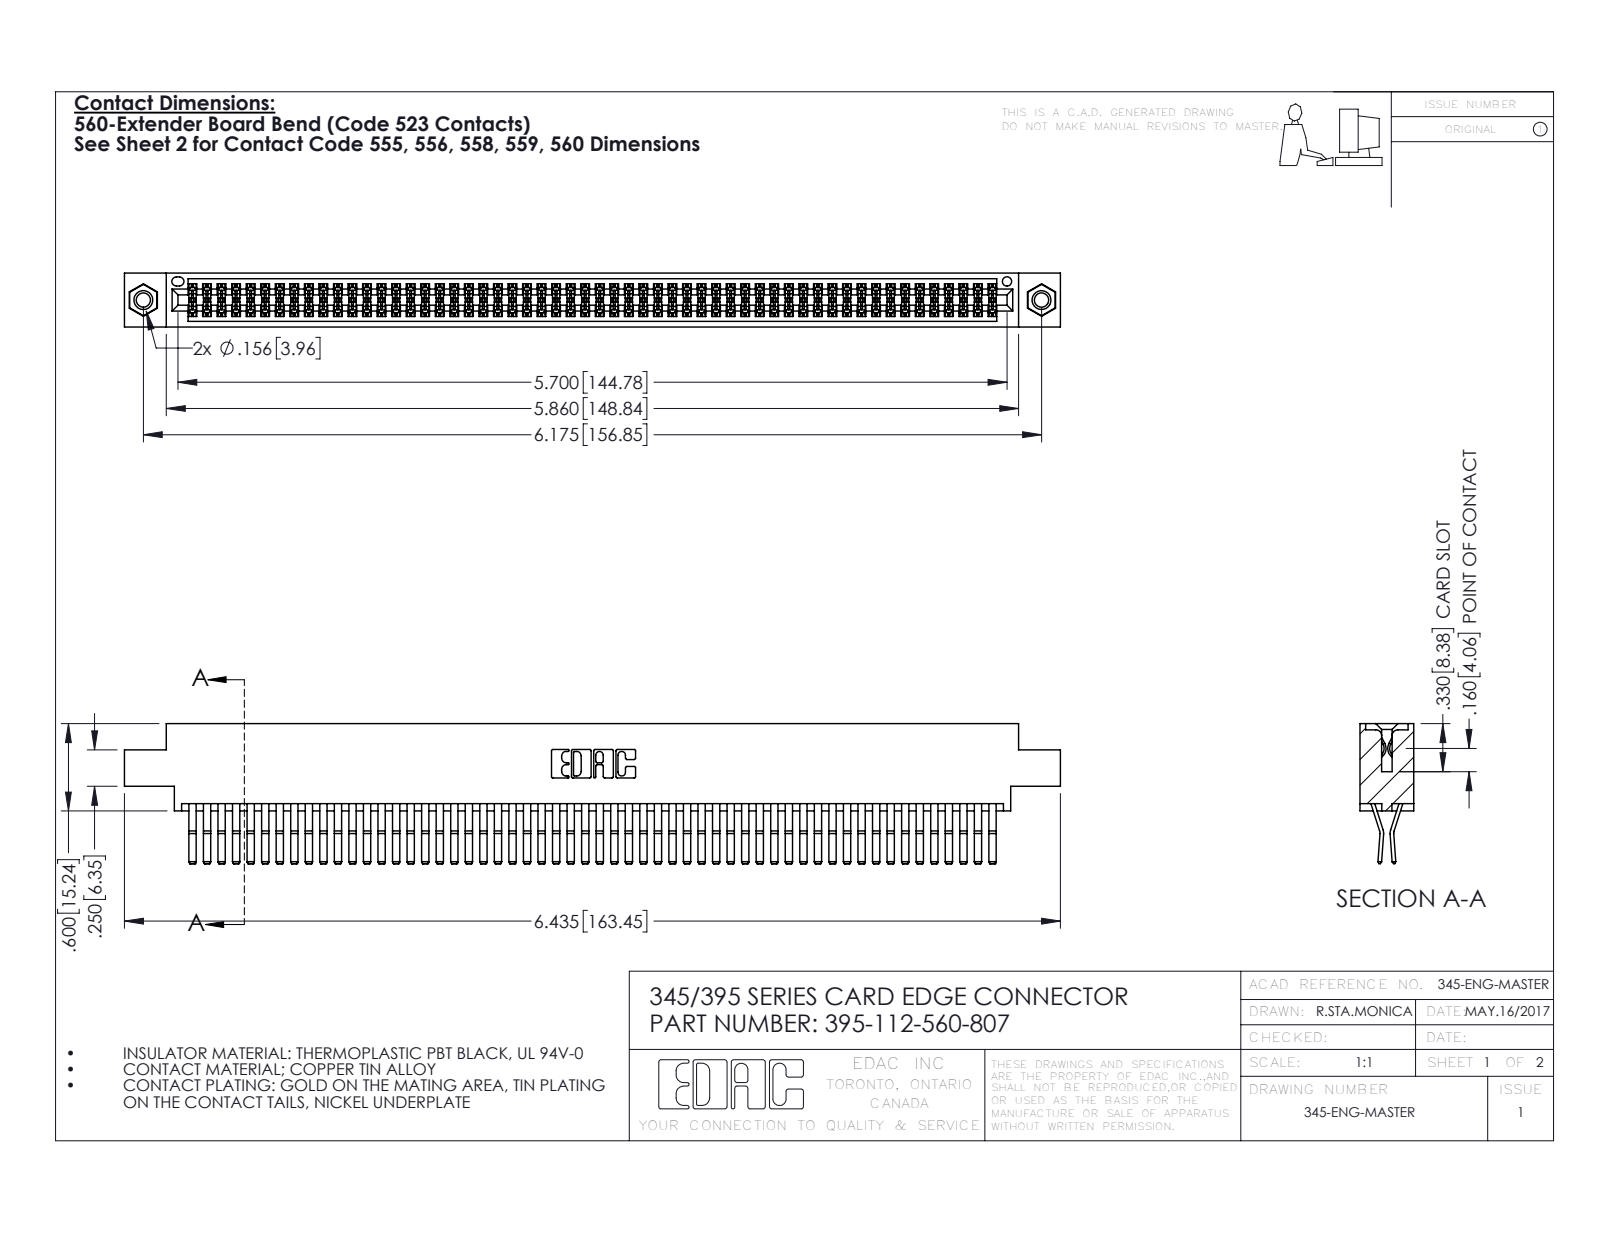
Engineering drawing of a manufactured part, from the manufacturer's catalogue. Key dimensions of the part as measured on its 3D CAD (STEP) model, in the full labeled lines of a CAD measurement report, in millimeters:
Part name (STEP PRODUCT): 345-250-001_345-250-005-103; 395-112-560-807; 345-292-001_560 Tail; 345 Part_0.170 Offset - 0.156 Dia-TI
STEP written by: SolidWorks 2016 (CONFIG_CONTROL_DESIGN)
Units: millimetres
Bodies: 115 solids, 6014 faces (3812 planar, 2186 cylindrical, 16 other)
Overall size (bounding box): 163.4 × 24.4 × 9.4
Volume: 16 620 mm³ · Surface area: 26 890 mm²
Round holes (diameter × count): ⌀2.5 ×2, ⌀3.2 ×2, ⌀4 ×2, ⌀1.6 ×1
Round bosses / shafts (diameter × count): ⌀3.9 ×2
Partial cylindrical surfaces — rounded edges, fillets, slot ends (radius × count): R0.2 ×168, R0.3 ×22, R0.2 ×6, R0.8 ×6, R0.7 ×3, R0.3 ×2, R0.4 ×2, R0.5 ×2
Main face-to-face distances: 0.6, 1.8, 7.6, 9.4, 5.1, 2.5, 6.9, 5.7, 4.4, 3.8
Hole centre spacings: 6.9, 150.9, 156.8
